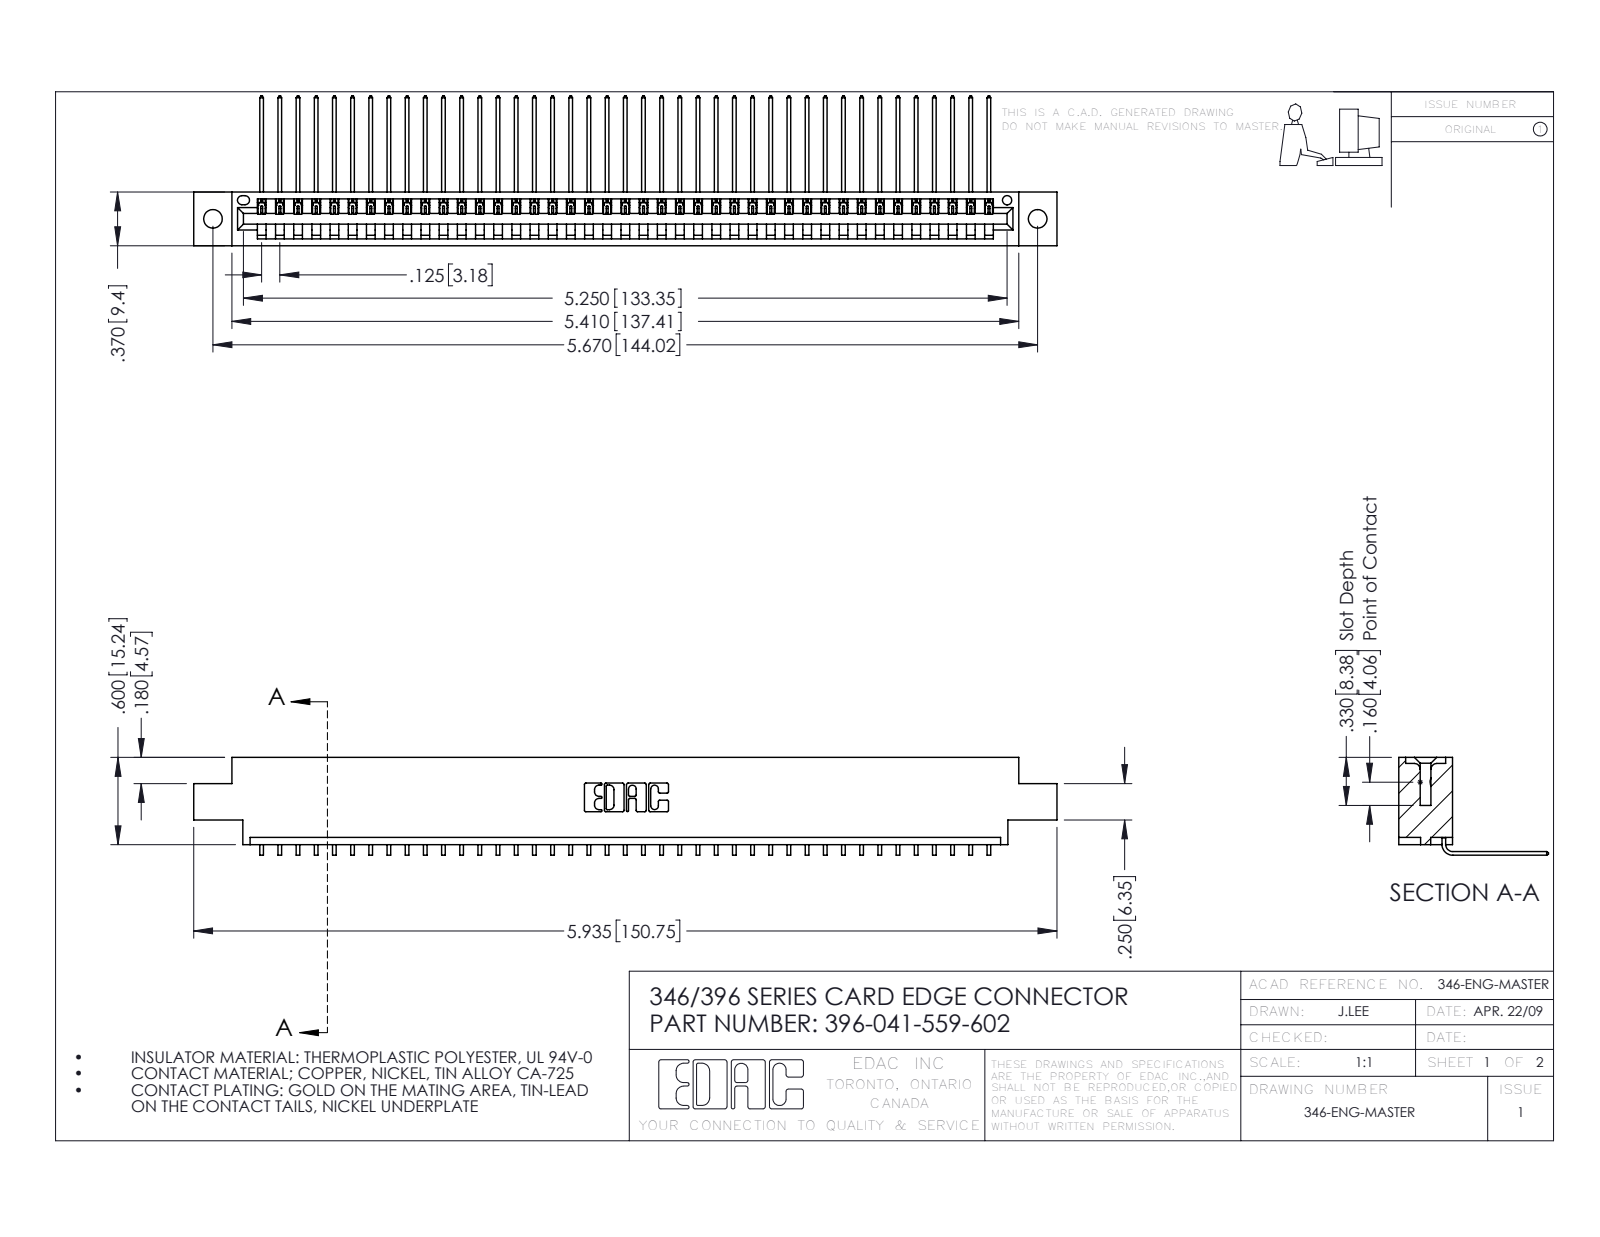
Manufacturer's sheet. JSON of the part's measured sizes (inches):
{"part_name": "396-041-559-602; 346 Part_0.170 Offset - 0.128 Dia; 345-292-001_558 559 Tail - 1", "step_written_by": "SolidWorks 2016 (CONFIG_CONTROL_DESIGN)", "units": "inches", "bodies": {"solids": 42, "faces": 2586, "planar": 1802, "cylindrical": 784, "other": 0}, "overall_size": [5.935, 1.03, 0.673], "volume_in3": 0.877, "surface_area_in2": 28.91, "round_holes": [[0.128, 2], [0.064, 1]], "partial_cylinders_radius": [[0.006, 82], [0.01, 22], [0.007, 6], [0.031, 6], [0.026, 3], [0.031, 2], [0.04, 2], [0.014, 1]], "face_to_face_distances": [0.048, 0.322, 0.37, 0.025, 0.25, 0.072, 0.298, 0.148, 0.222, 0.1], "hole_center_spacings": [0.246, 5.461, 5.67]}
